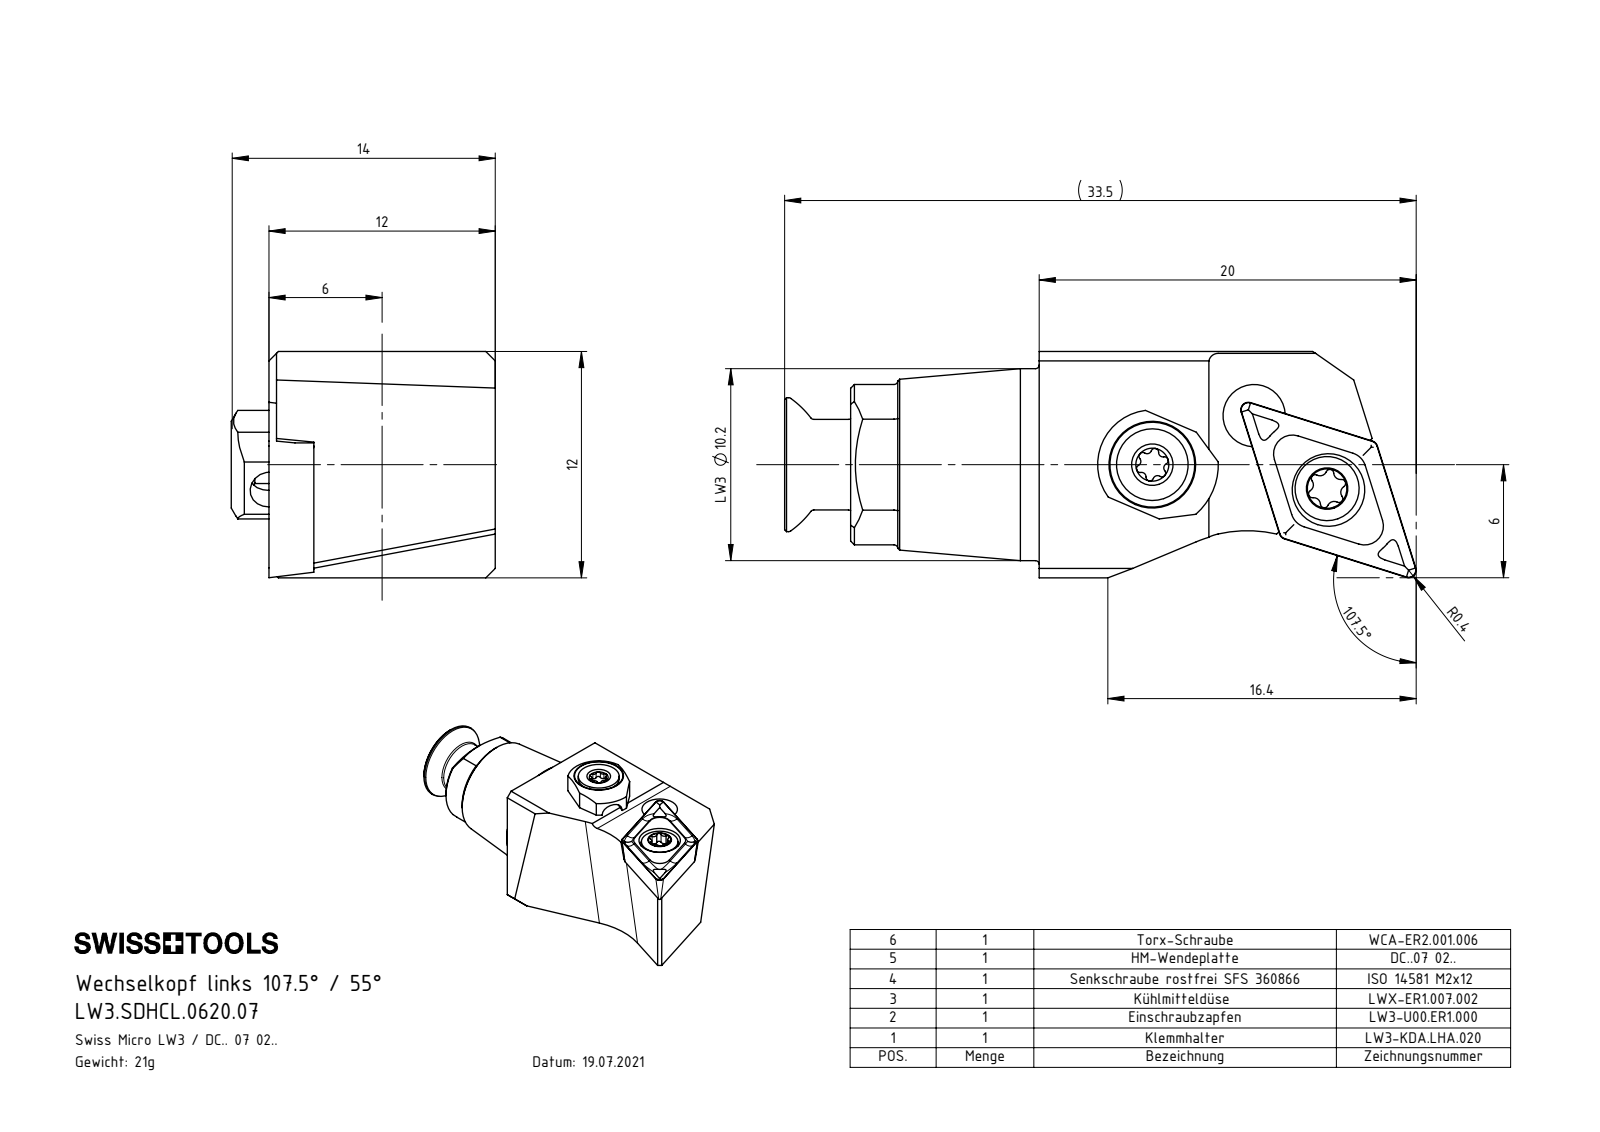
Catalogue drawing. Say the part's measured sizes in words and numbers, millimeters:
The part is named "LWX-ER1.007.002; LW3-U00.ER1.000_B; LW3-KDA.LHA.020_A; WCA-ER2.001.006_A (+3 more)". Its 3-D file was written by "SolidWorks 2022 (CONFIG_CONTROL_DESIGN)". It is 6 solids with 253 faces: 71 planar, 78 cylindrical and 104 other. Overall it measures 33.39 by 14 by 12 millimeters. Its volume is 2 731 cubic millimeters and its surface area 2 352 square millimeters. Round holes: 1 of diameter 1.6, 1 of diameter 2, 1 of diameter 2.05, 1 of diameter 2.5, 1 of diameter 2.8, 1 of diameter 3, 1 of diameter 3.3, 1 of diameter 3.85, 1 of diameter 5.5. Round bosses or shafts: 1 of diameter 10.18, 1 of diameter 6.9, 1 of diameter 6, 1 of diameter 5, 1 of diameter 4.8, 1 of diameter 3.8, 1 of diameter 3.4, 1 of diameter 2.5. Partial cylindrical surfaces (rounded edges, fillets, slot ends): 8 of radius 0.2, 6 of radius 0.21, 6 of radius 0.24, 4 of radius 0.36, 2 of radius 0.36, 1 of radius 0.5, 1 of radius 1, 1 of radius 2.9. The main face-to-face distances are 12, 9.62, 2.38, 2, 11.6, 1.98, 0.4, 2.5, 13.4, 11.4. The hole center spacings are 5.47, 5.57, 5.99, 9.36, 9.44.
